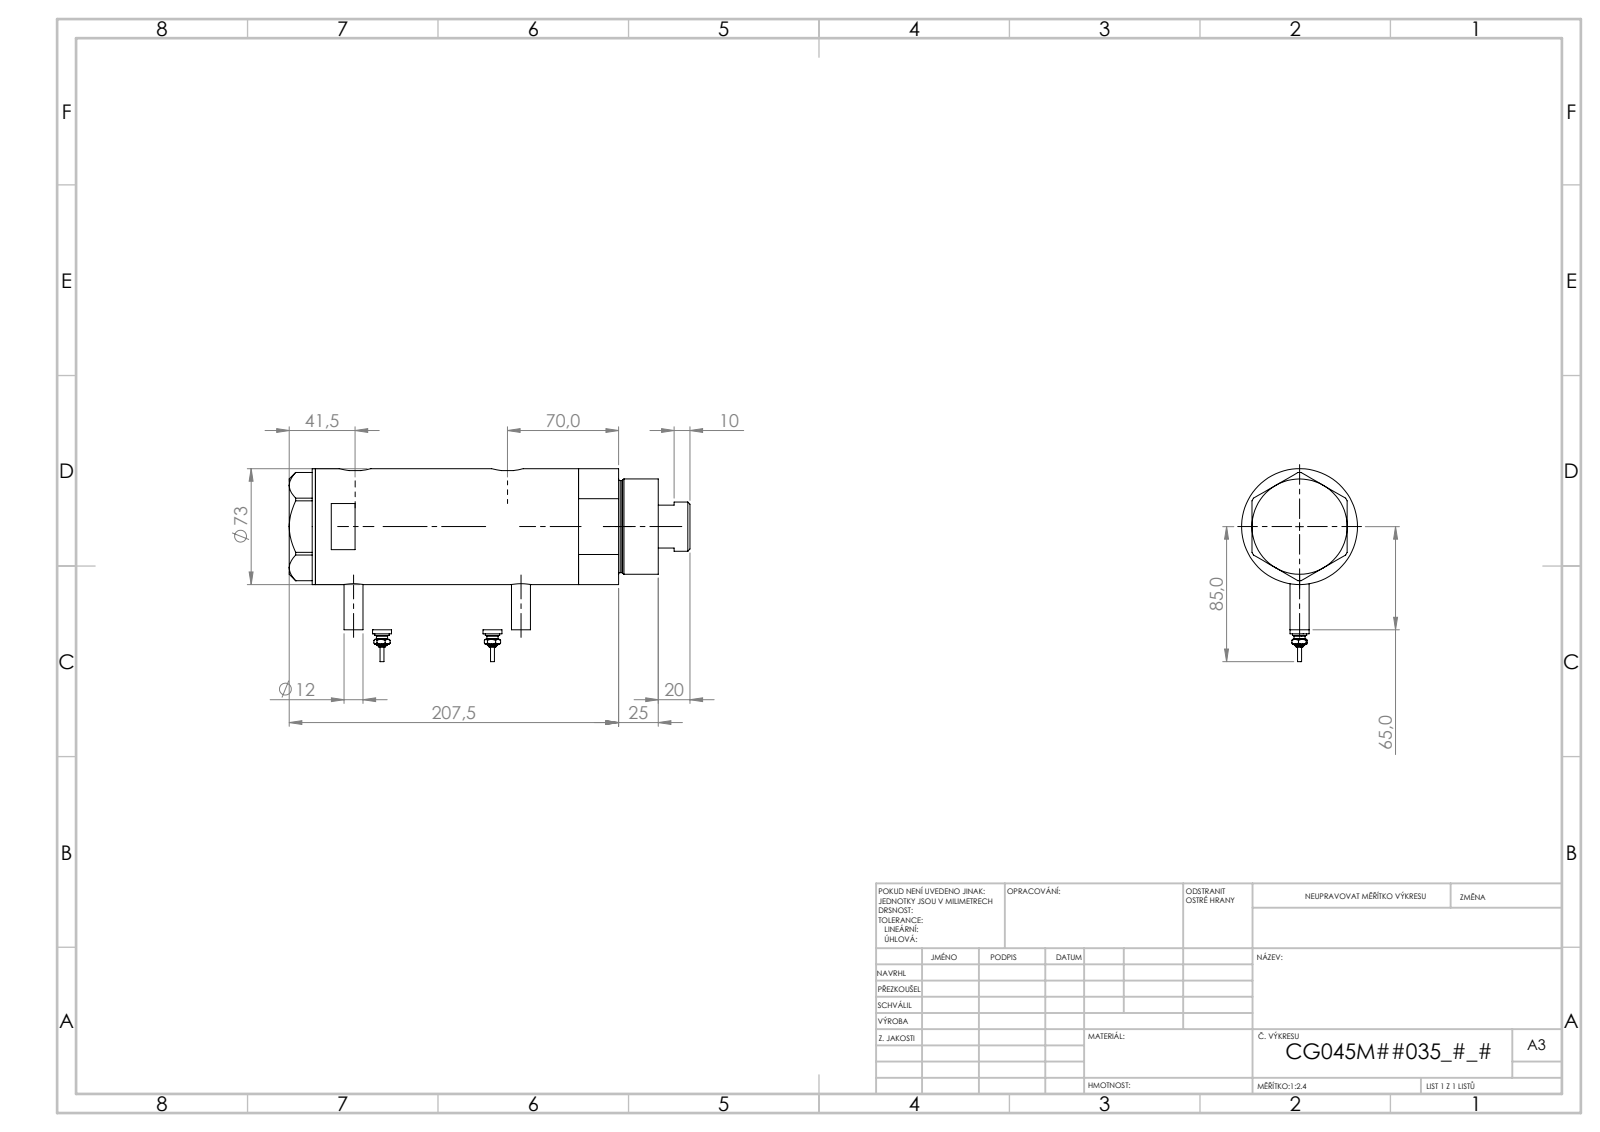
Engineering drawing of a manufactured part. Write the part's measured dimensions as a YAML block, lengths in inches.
part_name: "V270CG_FRONT; V270CG_VC; V270CG_MIDDLE; V270CG_BACK (+1 more)"
step_written_by: "SolidWorks 2019 (CONFIG_CONTROL_DESIGN)"
units: inches
bodies: {solids: 6, faces: 231, planar: 78, cylindrical: 79, other: 74}
overall_size: [8.918, 4.146, 2.874]
volume: 48.12
surface_area: 214.5
round_holes:
  - {diameter: 0.197, count: 2}
  - {diameter: 0.492, count: 2}
  - {diameter: 0.518, count: 2}
  - {diameter: 0.413, count: 1}
  - {diameter: 1.26, count: 1}
  - {diameter: 1.319, count: 1}
  - {diameter: 1.772, count: 1}
  - {diameter: 1.89, count: 1}
  - {diameter: 2.52, count: 1}
round_bosses_or_shafts:
  - {diameter: 0.472, count: 2}
  - {diameter: 0.354, count: 2}
  - {diameter: 0.276, count: 2}
  - {diameter: 0.197, count: 2}
  - {diameter: 0.171, count: 2}
  - {diameter: 0.094, count: 2}
  - {diameter: 2.874, count: 1}
  - {diameter: 2.362, count: 1}
partial_cylinders:
  - {radius: 0.394, count: 2}
face_to_face_distances: [2.998, 0.65, 4.671, 4.021, 7.481, 3.459, 6.457, 1.673, 1.024, 2.998]
hole_center_spacings: [3.411, 0.039, 0.039, 0.335, 0.335, 3.037, 3.076, 3.077]
